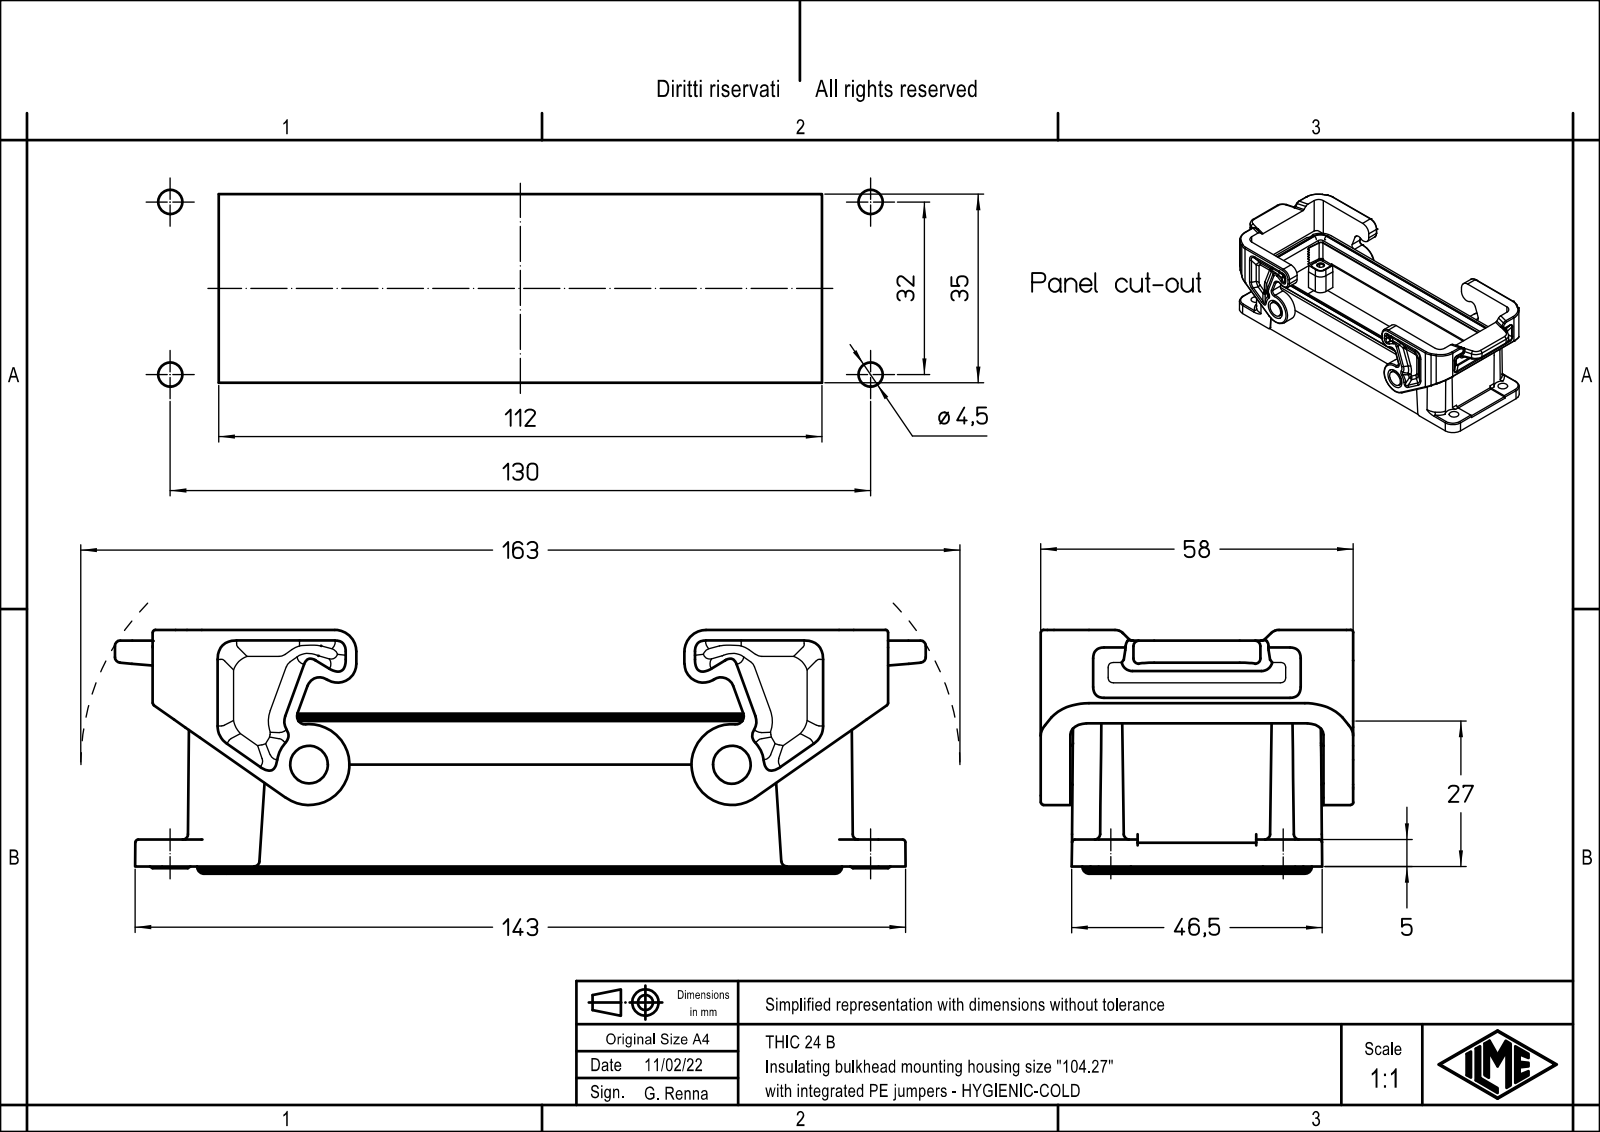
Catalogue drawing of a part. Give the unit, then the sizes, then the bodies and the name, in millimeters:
Units: millimetres
Overall size (bounding box): 150.5 × 58 × 45.25
Round holes (diameter × count): ⌀2.5 ×4, ⌀3.5 ×4, ⌀4.5 ×4, ⌀7.2 ×2
Round bosses / shafts (diameter × count): ⌀4.8 ×4, ⌀7 ×2
Partial cylindrical surfaces — rounded edges, fillets, slot ends (radius × count): R1 ×28, R1.5 ×22, R1.3 ×20, R2 ×16, R3 ×12, R5.5 ×12, R2.7 ×10, R5 ×8
Main face-to-face distances: 5.9, 41.1, 35.2, 40.4, 34.5, 6.6, 6.3, 34.8, 0.7, 40.7
Hole centre spacings: 13.24, 32.24, 117.03, 120.66, 27, 32, 104, 107.45
Volume: 79 020 mm³ · Surface area: 46 434 mm²
Bodies: 1 solid, 918 faces (474 planar, 260 cylindrical, 184 other)
Part name (STEP PRODUCT): 53623; THIH_24
STEP written by: Creo Elements/Direct Modeling 20.1B 02-Apr-2019 (C) Parametric Technology GmbH (AUTOMOTIVE_DESIGN)
